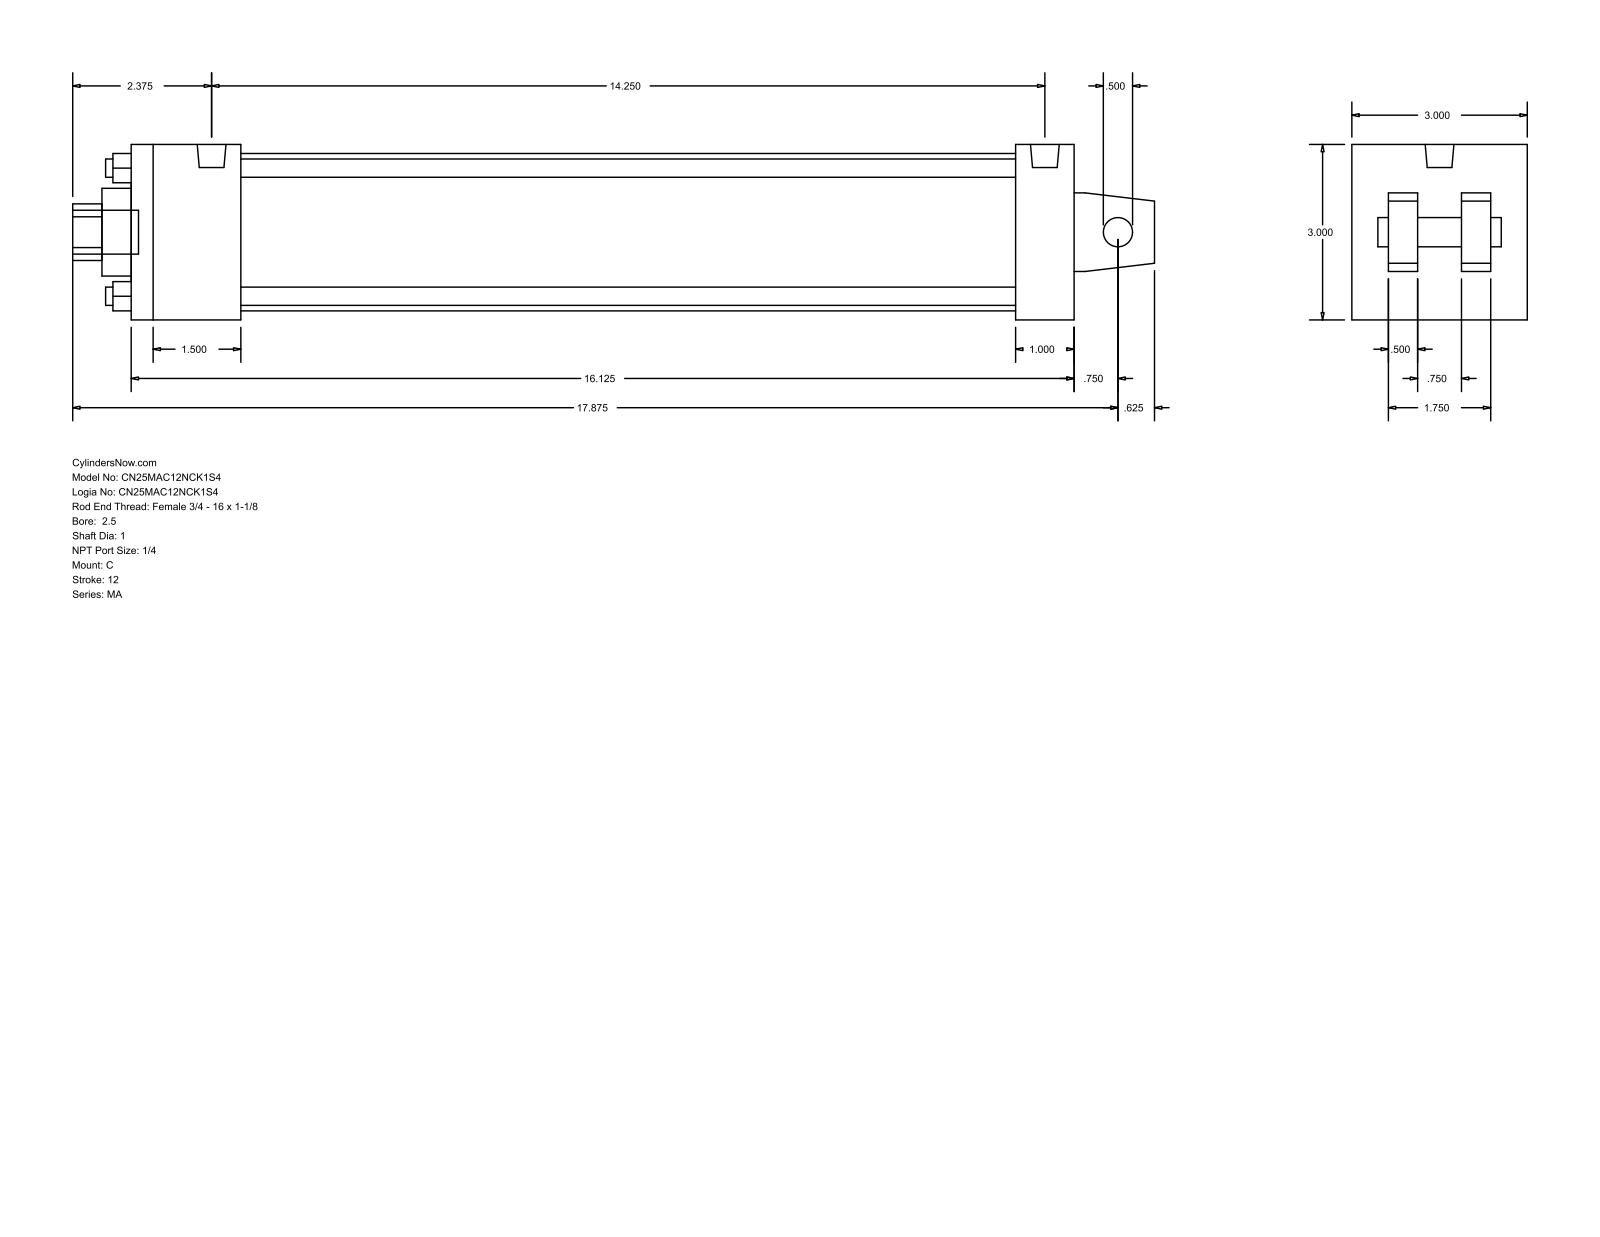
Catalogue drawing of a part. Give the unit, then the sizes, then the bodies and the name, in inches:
Units: inches
Overall size (bounding box): 18.5 × 3 × 3
Round holes (diameter × count): ⌀0.313 ×4, ⌀0.5 ×1, ⌀1 ×1, ⌀1.5 ×1, ⌀2.69 ×1
Round bosses / shafts (diameter × count): ⌀0.313 ×4, ⌀0.492 ×2, ⌀0.75 ×1
Partial cylindrical surfaces — rounded edges, fillets, slot ends (radius × count): R0.484 ×1
Main face-to-face distances: 3, 1.875, 16.125, 0.5, 2.375, 0.625, 1.125, 15.125, 13.25, 14.25
Hole centre spacings: 1.548, 2.19, 3.097
Bodies: 0 solids, 103 faces (76 planar, 27 cylindrical, 0 other)
Part name (STEP PRODUCT): MA_C__0250_1
STEP written by: GSSL Pune (CONFIG_CONTROL_DESIGN)
